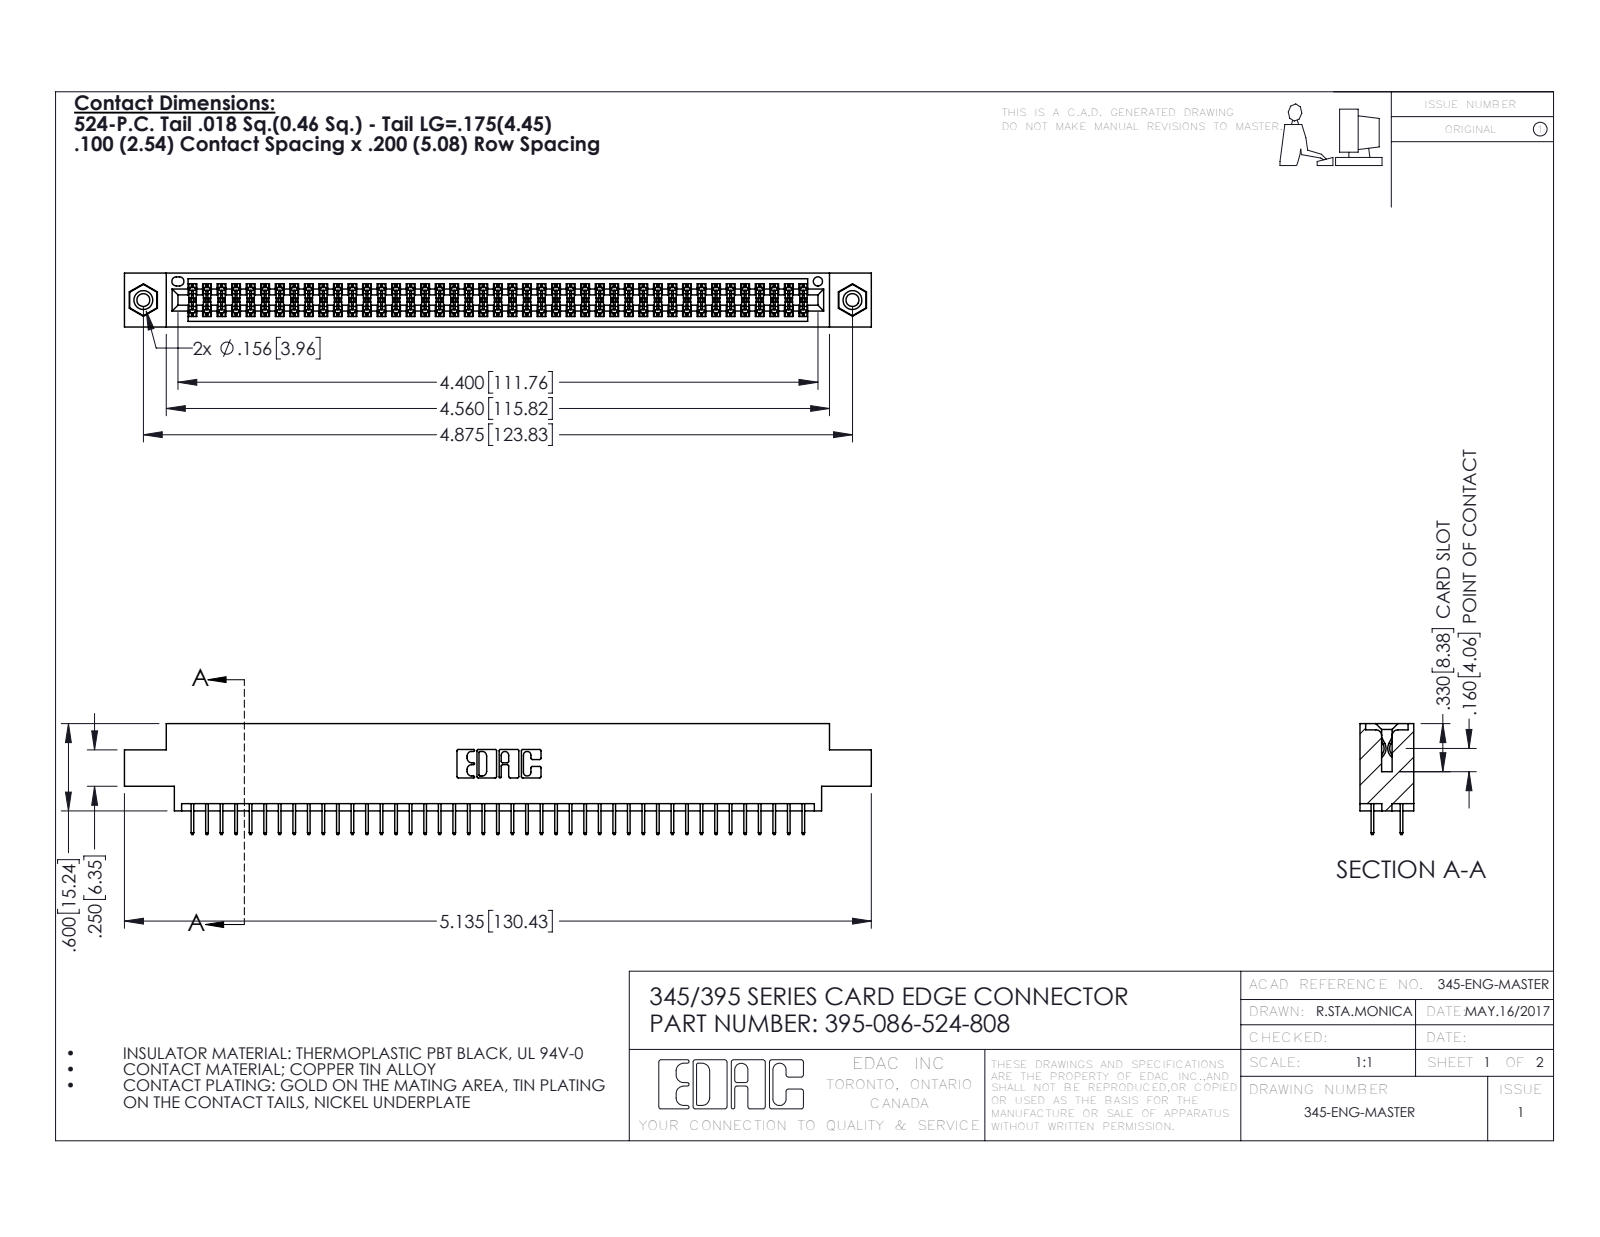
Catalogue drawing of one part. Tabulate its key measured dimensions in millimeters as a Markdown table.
| quantity | value |
| --- | --- |
| part name | 345-292-001_345-293-124; 345 Part_0.170 Offset - 0.156 Dia-TI; 395-086-524-808; 345-250-001_345-250-003-102 |
| STEP written by | SolidWorks 2016 (CONFIG_CONTROL_DESIGN) |
| units | millimeters |
| bodies | 89 solids, 4834 faces (3470 planar, 1348 cylindrical, 16 other) |
| overall size | 130.4 × 19.4 × 9.4 |
| volume | 12 400 mm³ |
| surface area | 18 210 mm² |
| round holes (diameter × count) | 2.3 × 2, 3.2 × 2, 4 × 2, 1.6 × 1 |
| round bosses / shafts (diameter × count) | 3.9 × 2 |
| partial cylindrical surfaces (radius × count) | 0.2 × 129, 0.3 × 22, 0.2 × 6, 0.8 × 6, 0.7 × 3, 0.4 × 2, 0.5 × 2, 0.6 × 2 |
| main face-to-face distances | 1.8, 7.6, 9.4, 5.1, 2.5, 6.9, 0.6, 5.7, 4.4, 1.8 |
| hole center spacings | 6.9, 117.8, 123.8 |
